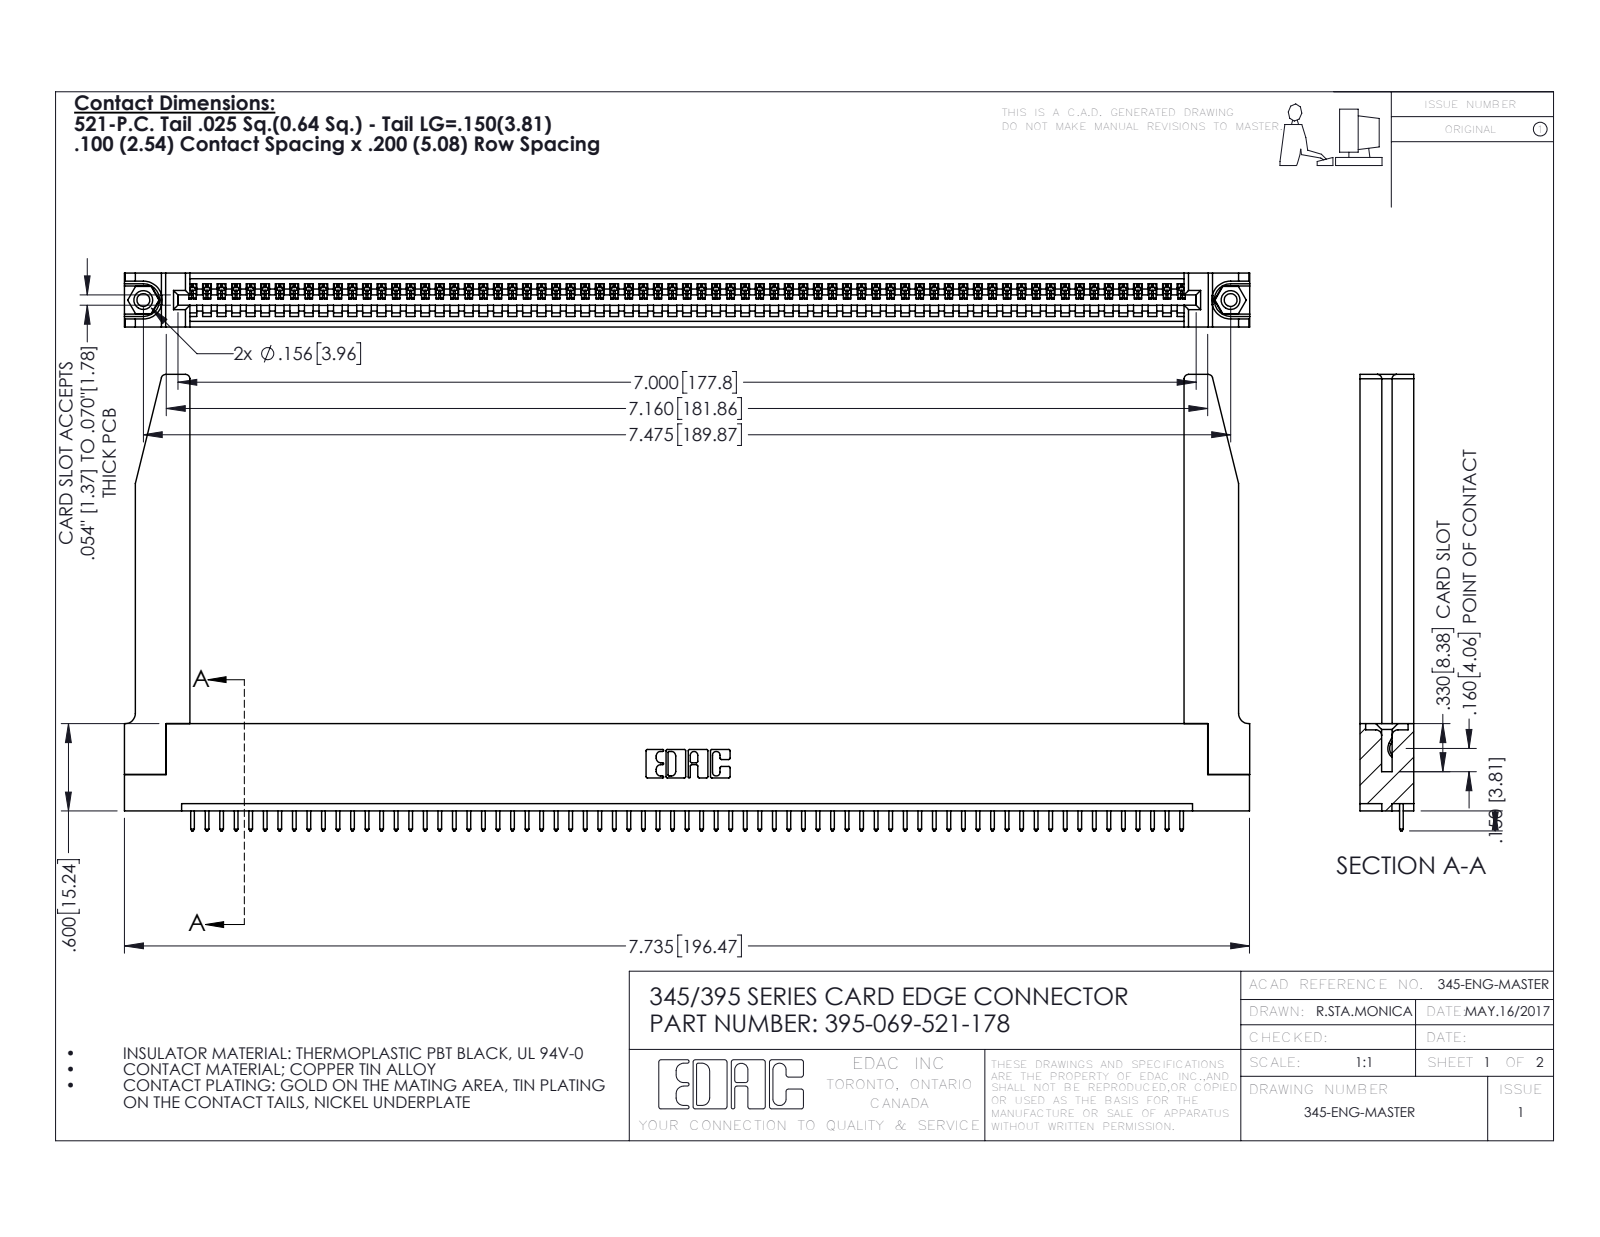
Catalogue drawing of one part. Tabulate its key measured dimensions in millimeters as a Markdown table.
| quantity | value |
| --- | --- |
| part name | 345-292-001_345-293-121; 395-069-521-178; 345-220-078_345-220-078; 345 Part_Flush Mounting Lugs - 0.156 Dia-TH (+1 more) |
| STEP written by | SolidWorks 2016 (CONFIG_CONTROL_DESIGN) |
| units | millimeters |
| bodies | 74 solids, 4362 faces (2982 planar, 1328 cylindrical, 52 other) |
| overall size | 196.5 × 79.7 × 9.4 |
| volume | 26 470 mm³ |
| surface area | 31 280 mm² |
| round holes (diameter × count) | 2.3 × 2, 3.2 × 2, 4 × 2, 1.6 × 1 |
| round bosses / shafts (diameter × count) | 3.9 × 2 |
| partial cylindrical surfaces (radius × count) | 0.2 × 138, 0.3 × 138, 0.3 × 22, 0.8 × 8, 0.2 × 6, 0.8 × 6, 0.7 × 3, 0.8 × 2 |
| main face-to-face distances | 1.8, 9.4, 7.6, 5.1, 2.5, 6.9, 0.6, 5.7, 3.8, 3.8 |
| hole center spacings | 6.9, 183.9, 189.9 |
